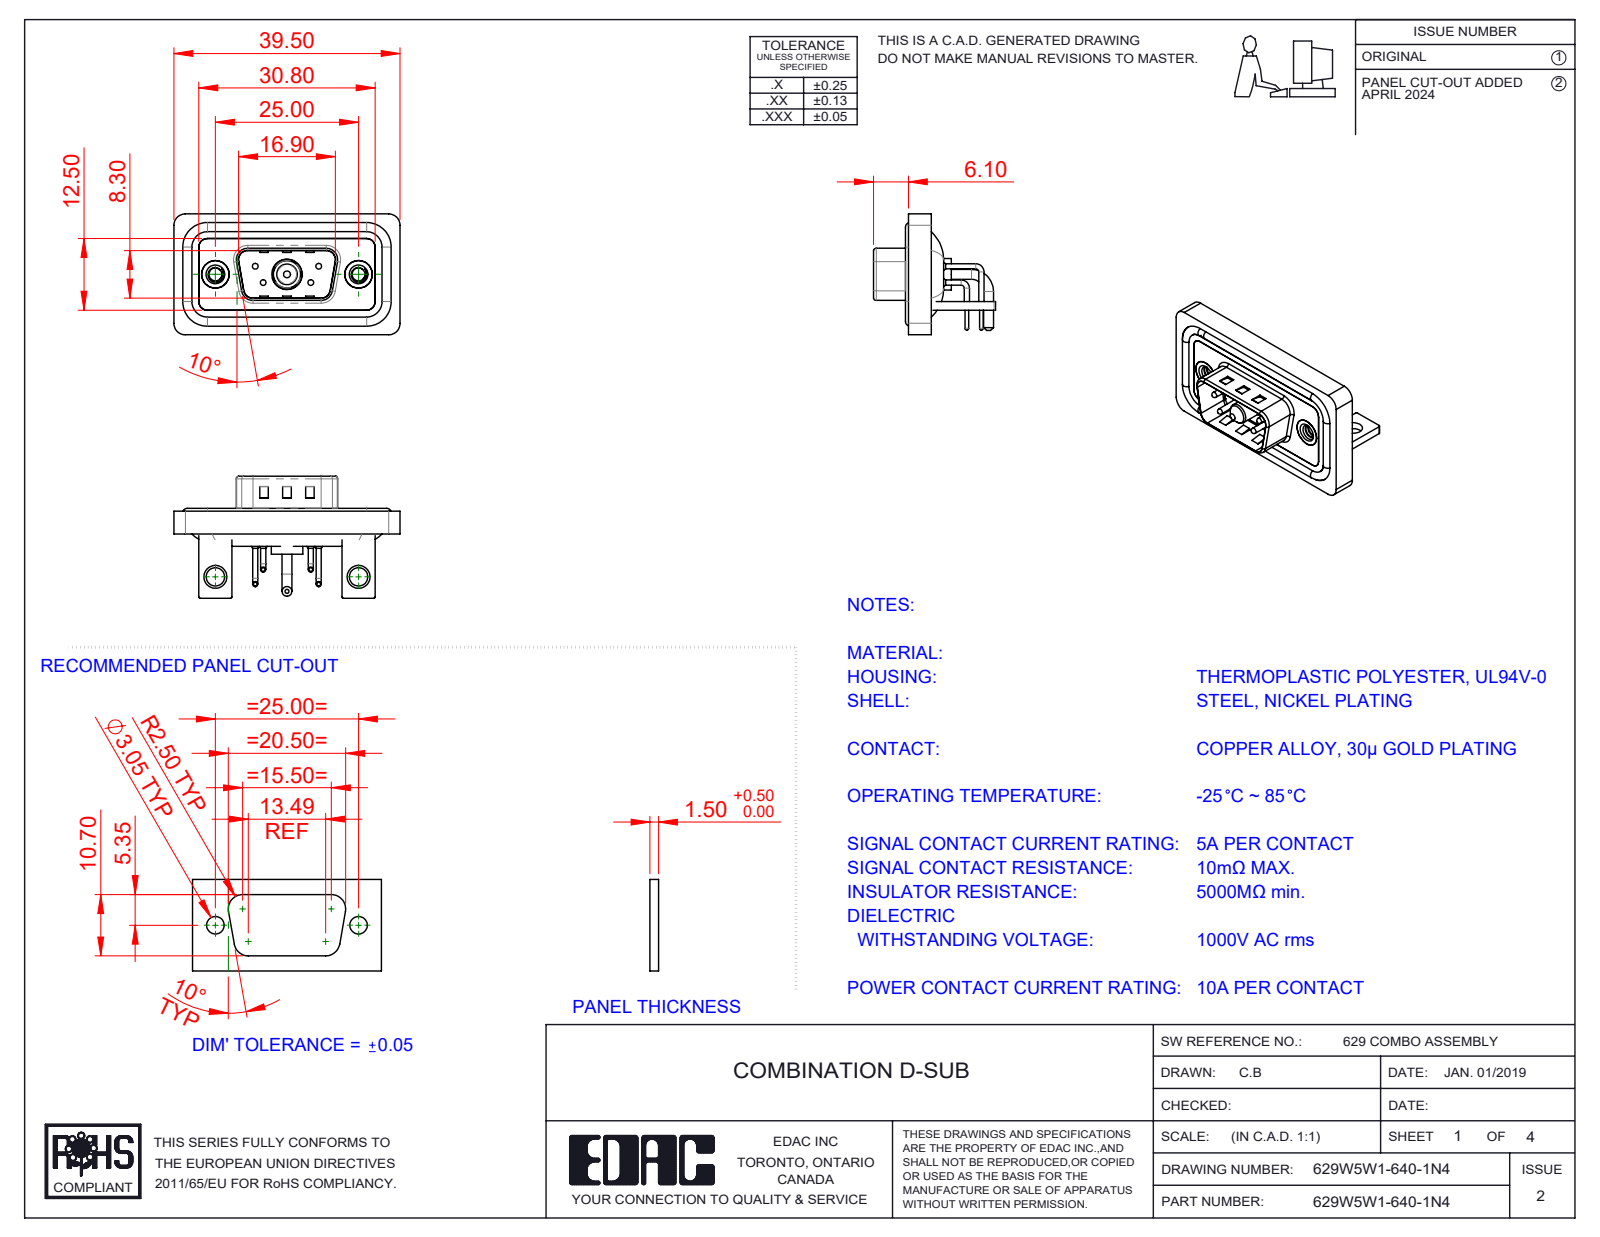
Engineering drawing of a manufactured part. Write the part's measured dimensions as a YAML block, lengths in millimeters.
part_name: "629W5W1-640-1N4; 629Combo Shell Rear_09 Contacts; 629Combo Shell Front_09 Contacts; 629Combo Waterproof Housing_09 Contacts (+6 more)"
step_written_by: "SolidWorks 2023 (CONFIG_CONTROL_DESIGN)"
units: millimeters
bodies: {solids: 15, faces: 934, planar: 431, cylindrical: 363, other: 140}
overall_size: [39.5, 21.3, 21.1]
volume: 4696
surface_area: 7700
round_holes:
  - {diameter: 0.75, count: 4}
  - {diameter: 1.6, count: 4}
  - {diameter: 2, count: 4}
  - {diameter: 2.26, count: 2}
  - {diameter: 3.2, count: 2}
  - {diameter: 4, count: 2}
  - {diameter: 4.8, count: 2}
  - {diameter: 5, count: 2}
  - {diameter: 4.85, count: 1}
  - {diameter: 5.3, count: 1}
round_bosses_or_shafts:
  - {diameter: 0.9, count: 8}
  - {diameter: 1.6, count: 4}
  - {diameter: 1.5, count: 4}
  - {diameter: 1, count: 4}
  - {diameter: 0.65, count: 4}
  - {diameter: 4.9, count: 2}
  - {diameter: 1.7, count: 2}
  - {diameter: 5.5, count: 1}
partial_cylinders:
  - {radius: 2, count: 19}
  - {radius: 1.5, count: 18}
  - {radius: 0.25, count: 16}
  - {radius: 0.5, count: 9}
  - {radius: 1.6, count: 8}
  - {radius: 0.6, count: 4}
  - {radius: 0.65, count: 4}
  - {radius: 0.9, count: 4}
face_to_face_distances: [0.4, 1.5, 0.8, 2.9, 1.1, 2.1, 1.2, 1.6, 2.5, 3.7]
hole_center_spacings: [3.16, 5.72, 7.1, 12.5, 18.1, 25, 4.39, 4.4]
